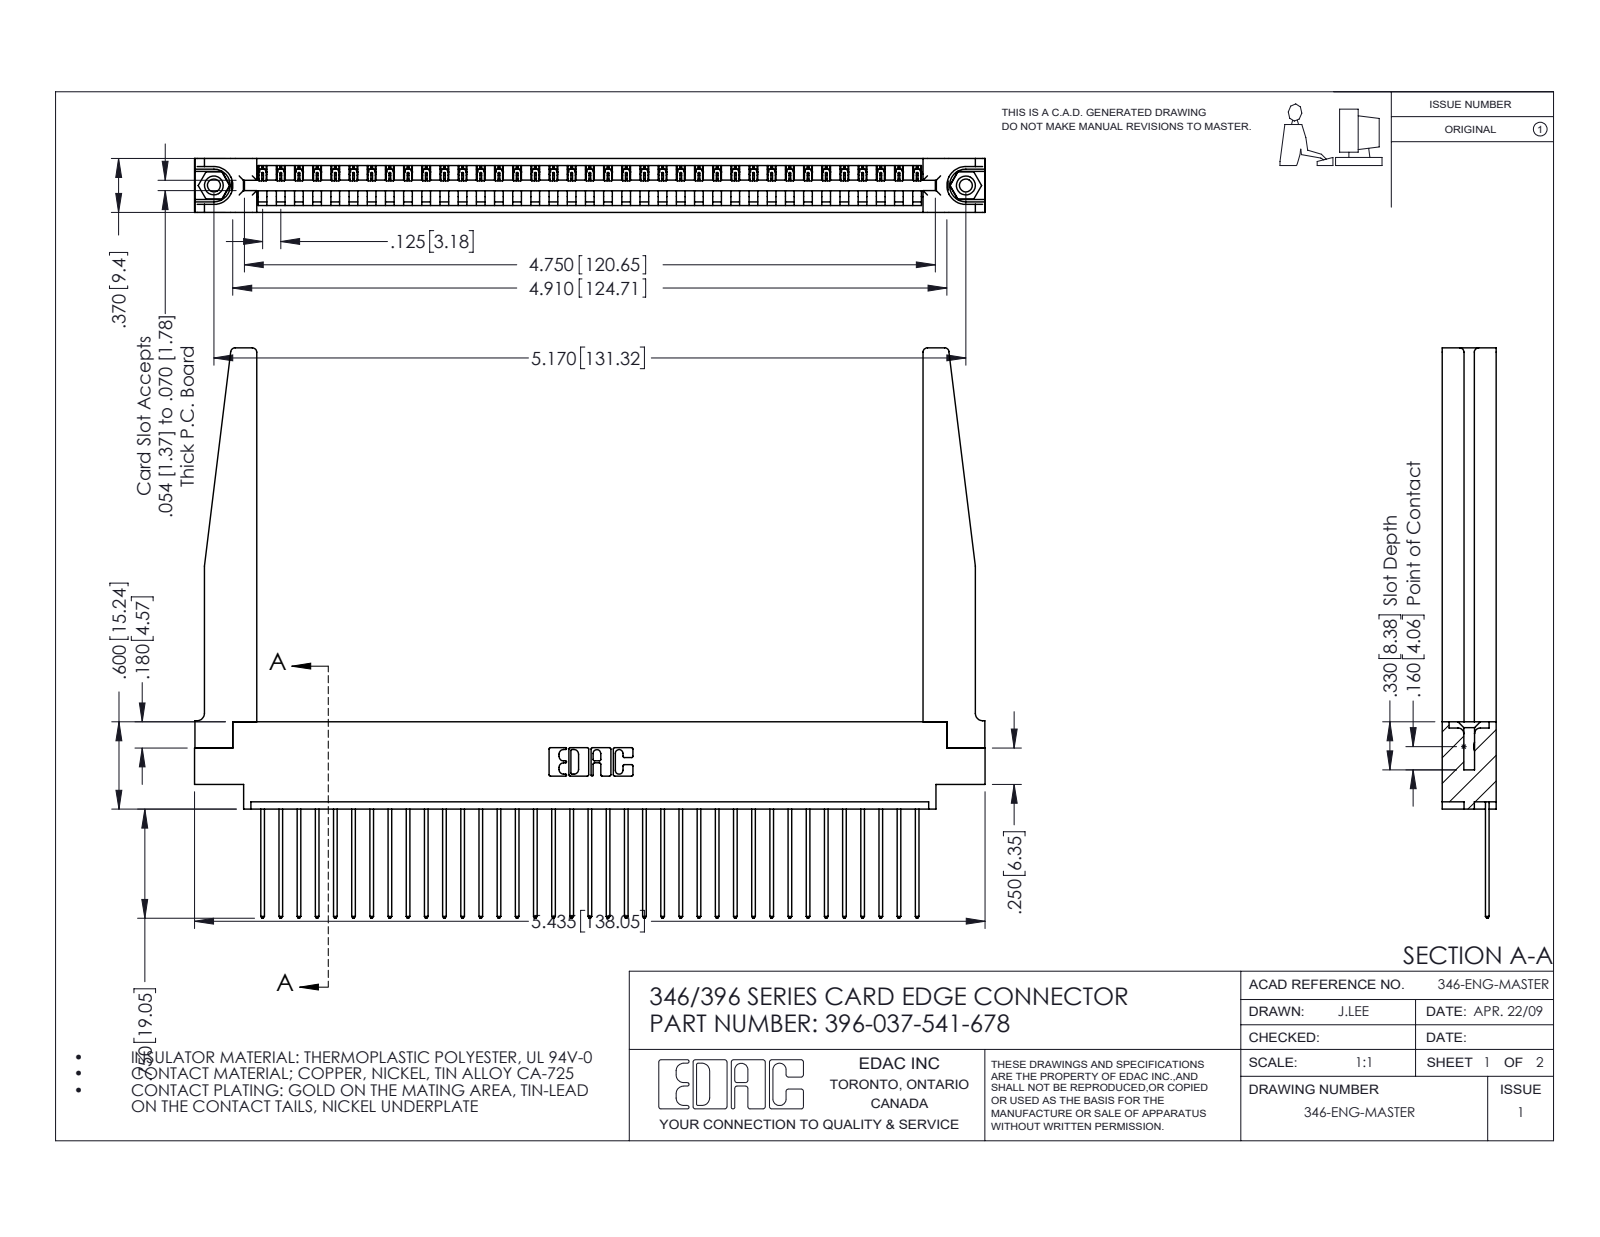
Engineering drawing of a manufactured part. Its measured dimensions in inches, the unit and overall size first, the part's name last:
Units: inches
Overall size (bounding box): 5.435 × 3.92 × 0.37
Round holes (diameter × count): ⌀0.089 ×2, ⌀0.125 ×2, ⌀0.156 ×2, ⌀0.064 ×1
Round bosses / shafts (diameter × count): ⌀0.155 ×2
Partial cylindrical surfaces — rounded edges, fillets, slot ends (radius × count): R0.006 ×74, R0.01 ×74, R0.01 ×22, R0.03 ×8, R0.007 ×6, R0.031 ×6, R0.026 ×3, R0.031 ×2
Main face-to-face distances: 0.37, 0.048, 0.322, 0.072, 0.148, 0.15, 0.25, 0.298, 0.025, 0.222
Hole centre spacings: 0.246, 4.961, 5.17
Volume: 1.224 in³ · Surface area: 36.9 in²
Bodies: 42 solids, 2506 faces (1702 planar, 752 cylindrical, 52 other)
Part name (STEP PRODUCT): 346 Part_0.170 Offset - 0.156 Dia-TH; 396-037-541-678; 345-292-001_345-293-141; 345-250-001_345-250-001-102 (+1 more)
STEP written by: SolidWorks 2016 (CONFIG_CONTROL_DESIGN)
